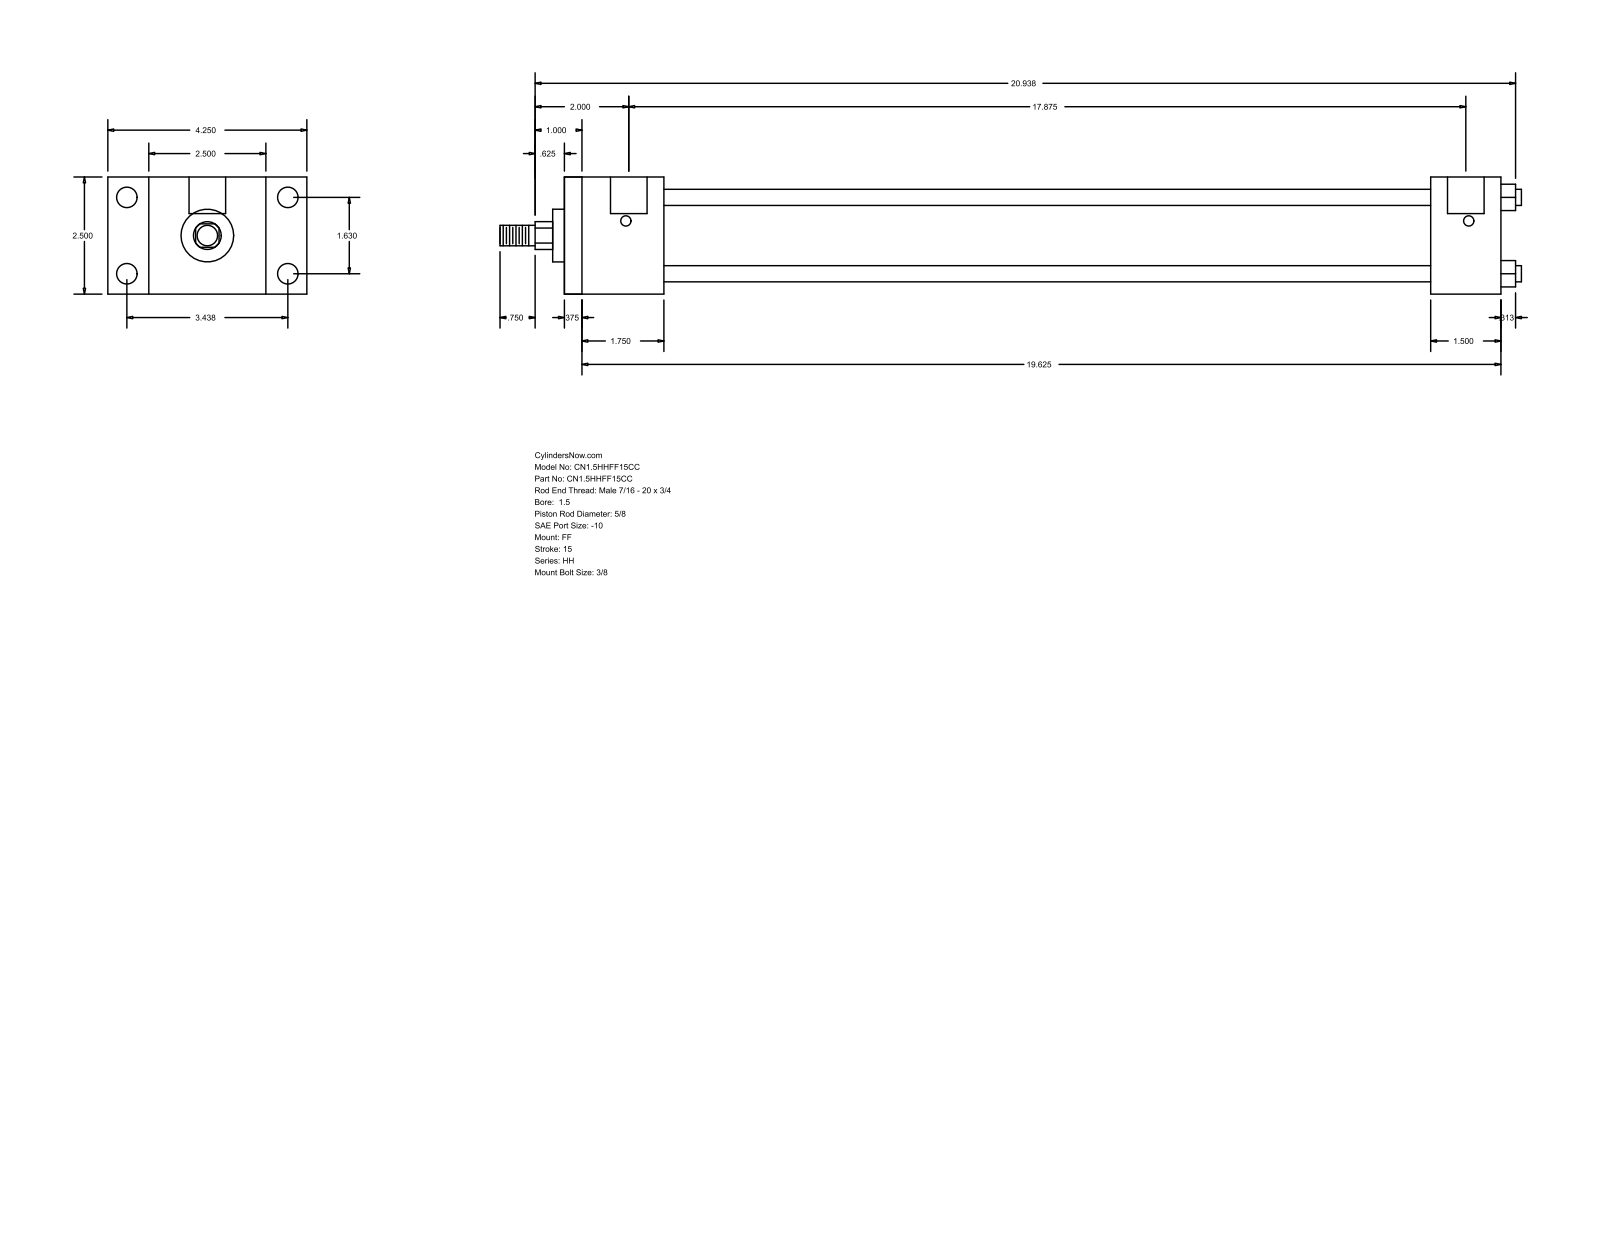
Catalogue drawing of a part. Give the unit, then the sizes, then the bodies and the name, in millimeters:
Units: millimetres
Overall size (bounding box): 554.04 × 107.95 × 63.5
Round holes (diameter × count): ⌀5.56 ×4, ⌀11.13 ×4, ⌀19.84 ×2
Round bosses / shafts (diameter × count): ⌀8.76 ×4, ⌀44.45 ×1, ⌀28.57 ×1, ⌀15.88 ×1, ⌀11.11 ×1
Partial cylindrical surfaces — rounded edges, fillets, slot ends (radius × count): R7.54 ×1
Main face-to-face distances: 63.5, 508, 9.52, 498.48, 44.45, 53.97, 454.03, 469.89, 460.37, 415.92
Hole centre spacings: 1.59, 41.4, 87.32, 96.64, 455.61, 457.2, 454.02
Bodies: 0 solids, 92 faces (64 planar, 28 cylindrical, 0 other)
Part name (STEP PRODUCT): HH_FF__0150_0.625
STEP written by: GSSL Pune (CONFIG_CONTROL_DESIGN)
